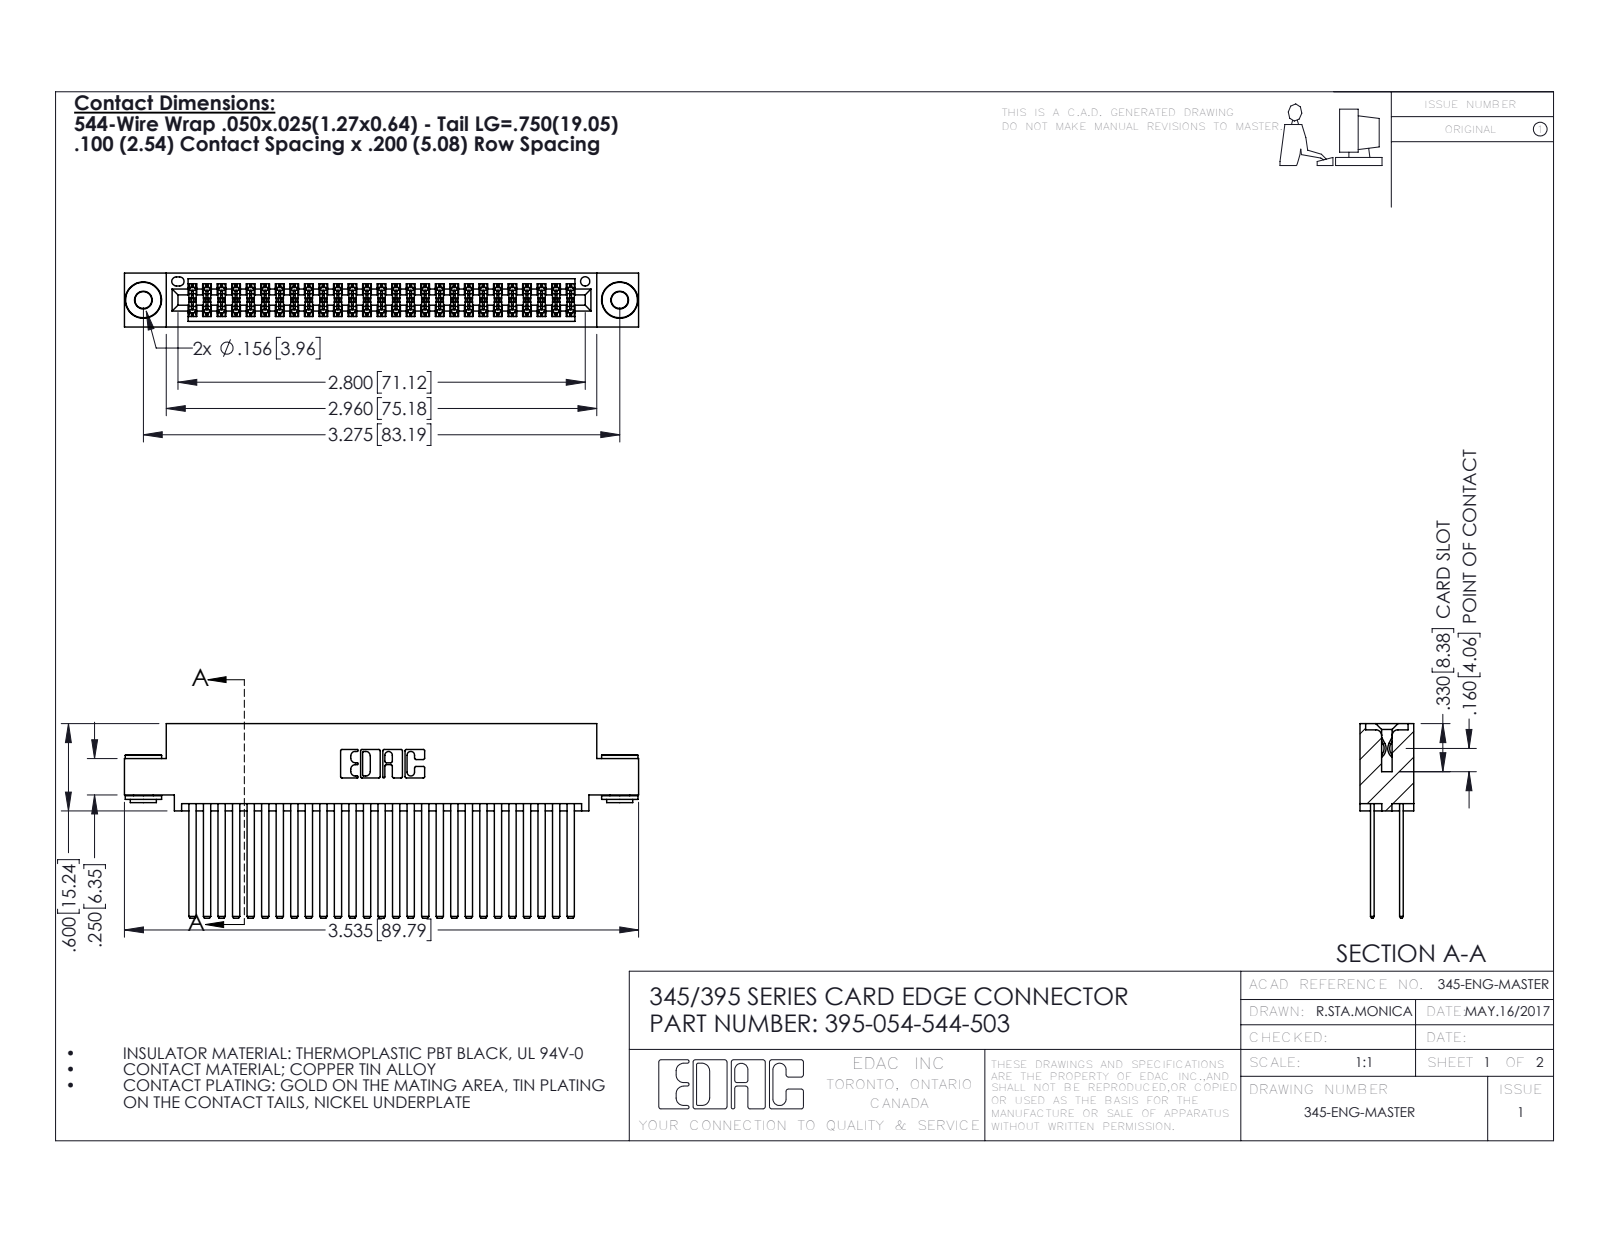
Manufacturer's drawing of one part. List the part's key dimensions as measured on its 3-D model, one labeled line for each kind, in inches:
Part name (STEP PRODUCT): 345-292-001_345-293-144; 345-250-002_345-250-002-102; 395-054-544-503; 345 Part_0.110 Offset - 0.156 Dia-TH
STEP written by: SolidWorks 2016 (CONFIG_CONTROL_DESIGN)
Units: inches
Bodies: 57 solids, 2544 faces (1660 planar, 876 cylindrical, 8 other)
Overall size (bounding box): 3.535 × 1.337 × 0.37
Volume: 0.567 in³ · Surface area: 24.73 in²
Round holes (diameter × count): ⌀0.116 ×2, ⌀0.156 ×2, ⌀0.064 ×1
Round bosses / shafts (diameter × count): ⌀0.25 ×2, ⌀0.18 ×2, ⌀0.136 ×2
Partial cylindrical surfaces — rounded edges, fillets, slot ends (radius × count): R0.006 ×81, R0.01 ×22, R0.007 ×6, R0.031 ×6, R0.026 ×3, R0.014 ×2, R0.019 ×2, R0.022 ×2
Main face-to-face distances: 0.2, 0.025, 0.072, 0.298, 0.098, 0.272, 0.225, 0.175, 0.37, 0.05
Hole centre spacings: 0.27, 3.04, 3.275
